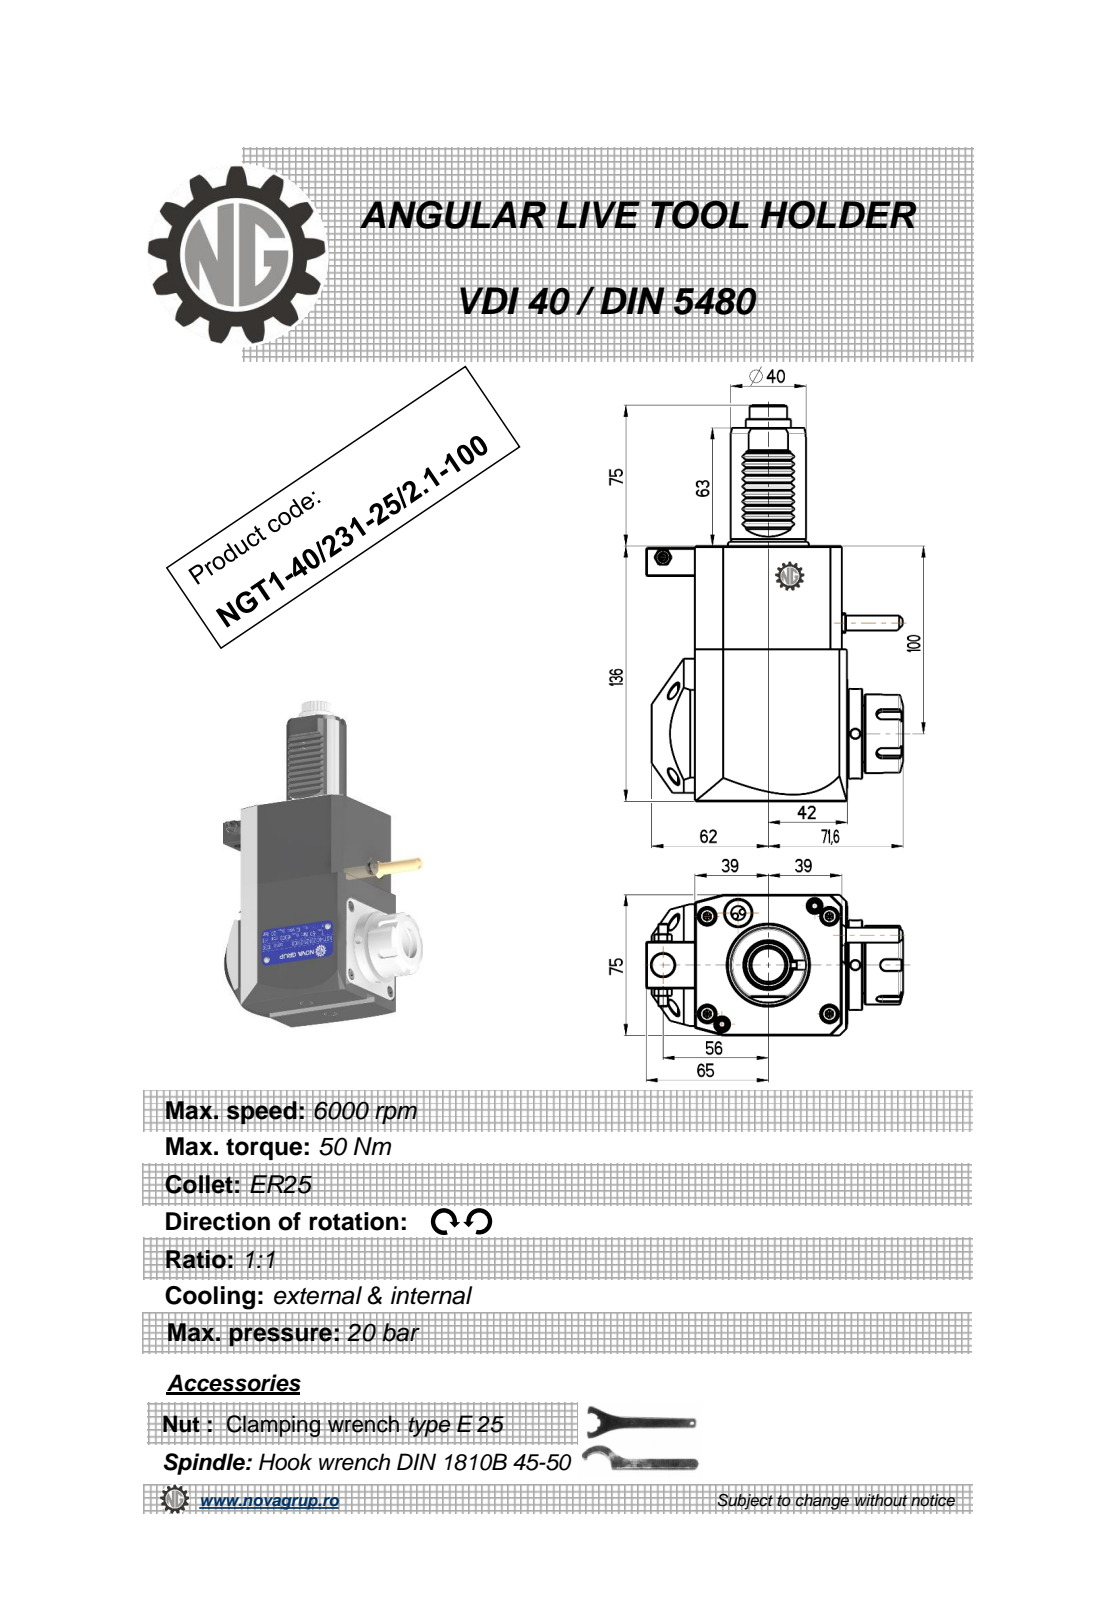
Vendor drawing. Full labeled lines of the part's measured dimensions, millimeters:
Part name (STEP PRODUCT): NGT1_40_231_25_2_1_100
STEP written by: PRO/ENGINEER BY PARAMETRIC TECHNOLOGY CORPORATION, 2010280 (CONFIG_CONTROL_DESIGN)
Units: millimetres
Bodies: 1 solid, 555 faces (194 planar, 185 cylindrical, 176 other)
Overall size (bounding box): 211 × 136.6 × 76.6
Volume: 993 152 mm³ · Surface area: 76 479 mm²
Round holes (diameter × count): ⌀5 ×3, ⌀3 ×1, ⌀4.2 ×1, ⌀9.5 ×1, ⌀12 ×1, ⌀20.3 ×1
Round bosses / shafts (diameter × count): ⌀48 ×1, ⌀42 ×1, ⌀40 ×1, ⌀37.5 ×1, ⌀33 ×1, ⌀24 ×1, ⌀11.2 ×1, ⌀8.96 ×1
Partial cylindrical surfaces — rounded edges, fillets, slot ends (radius × count): R2.08 ×48, R0.26 ×12, R0.3 ×10, R0.22 ×6, R3 ×5, R9.08 ×1, R9.92 ×1, R15 ×1
Main face-to-face distances: 75, 136, 78, 81, 3, 80.8, 2.8, 7.5, 0.5, 11
Hole centre spacings: 36.22, 61.13, 91.5, 102.25, 138.89
